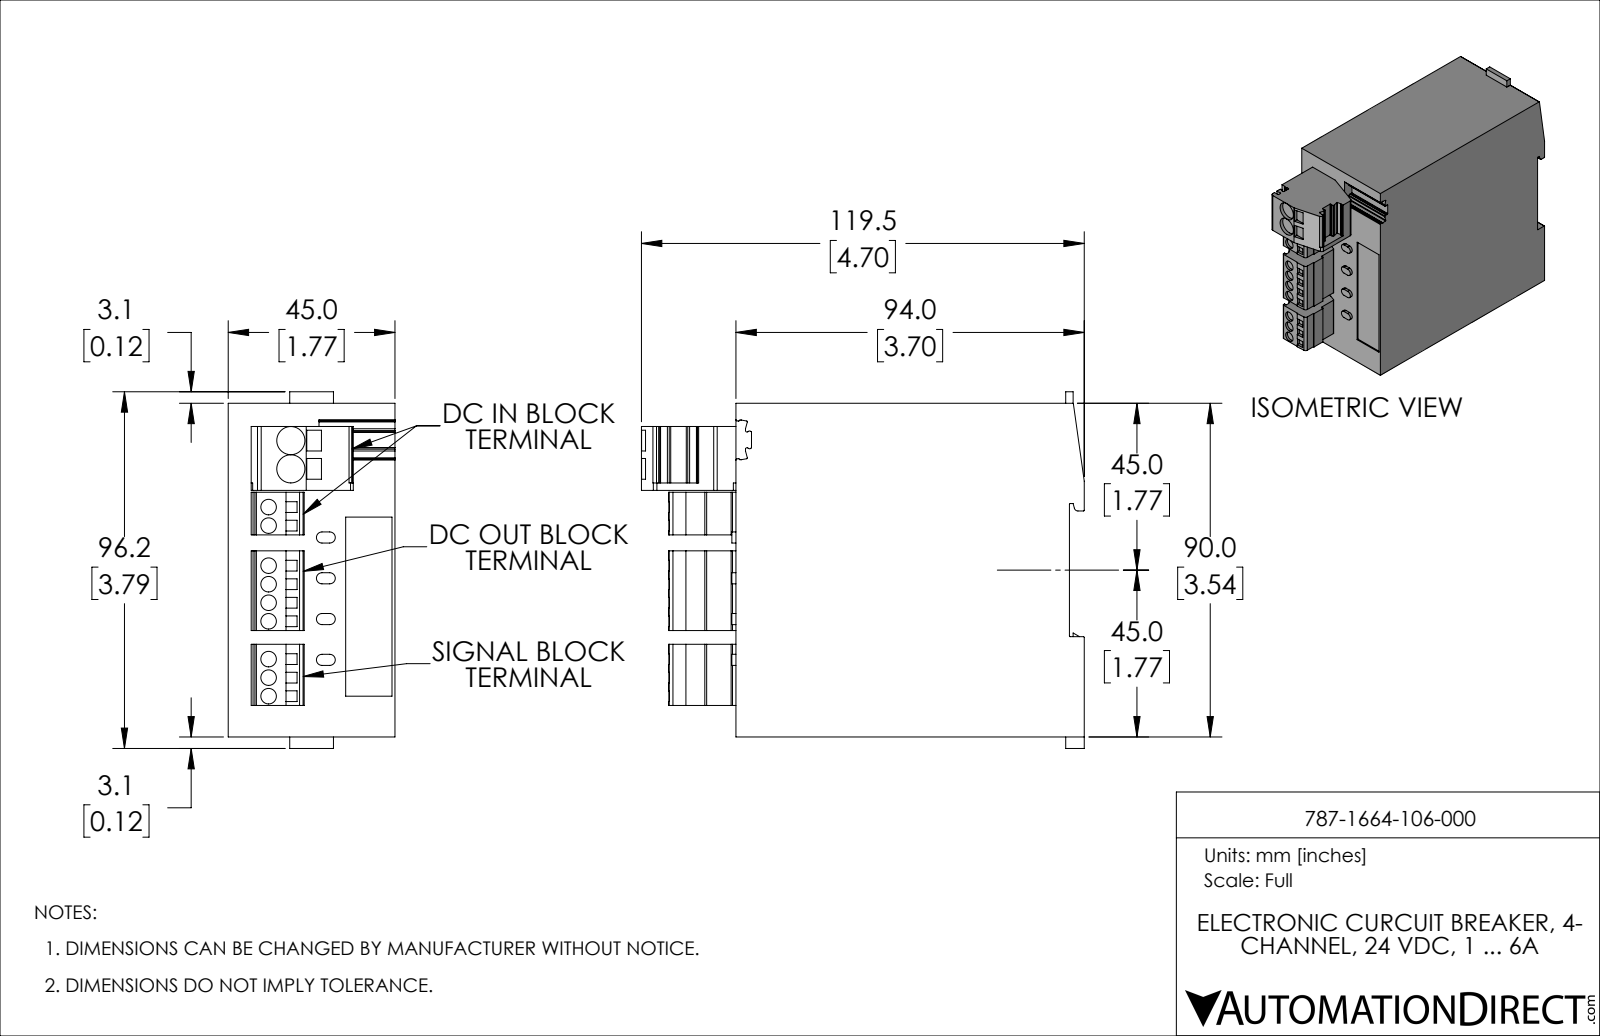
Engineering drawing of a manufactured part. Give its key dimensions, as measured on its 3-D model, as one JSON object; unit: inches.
{"part_name": "787-1664/106-000", "step_written_by": "PARTsolutions (CONFIG_CONTROL_DESIGN)", "units": "inches", "bodies": {"solids": 1, "faces": 328, "planar": 248, "cylindrical": 80, "other": 0}, "overall_size": [4.705, 3.787, 1.772], "volume_in3": 23.99, "surface_area_in2": 63.98, "round_holes": [[0.165, 9], [0.299, 2]], "partial_cylinders_radius": [[0.008, 25], [0.059, 8], [0.039, 7], [0.016, 6], [0.012, 4], [0.019, 4], [0.079, 1]], "face_to_face_distances": [1.772, 3.543, 0.157, 3.701, 0.02, 1.528, 0.244, 0.925, 2.618, 0.65], "hole_center_spacings": [0.197, 0.394, 0.795, 0.992, 0.598, 0.622, 0.819, 1.016]}
